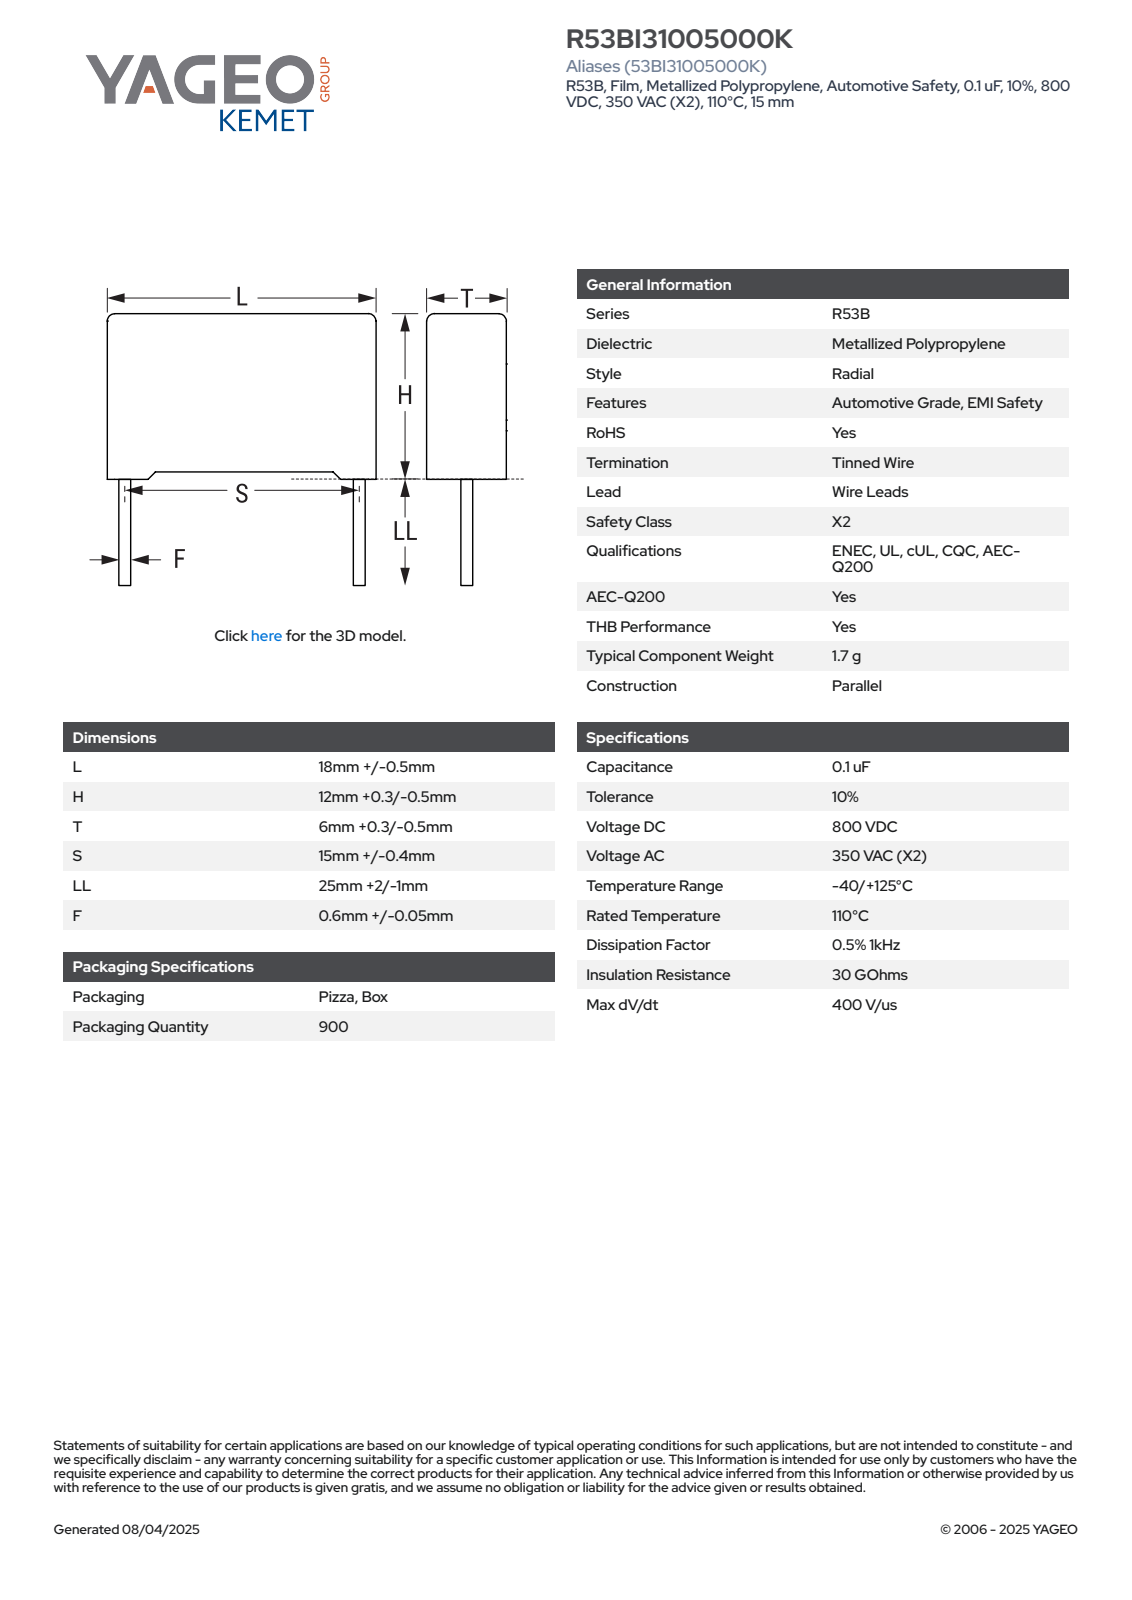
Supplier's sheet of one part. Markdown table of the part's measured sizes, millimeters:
| quantity | value |
| --- | --- |
| part name | CFR_RB2_18X12X6_L18.5H12.3T6.3S15LL27F0.65 |
| STEP written by | SolidWorks 2021 (AUTOMOTIVE_DESIGN) |
| units | millimeters |
| bodies | 4 solids, 85 faces (77 planar, 8 cylindrical, 0 other) |
| overall size | 39.3 × 18.5 × 6.3 |
| volume | 1 378 mm³ |
| surface area | 986 mm² |
| round bosses / shafts (diameter × count) | 0.65 × 2 |
| partial cylindrical surfaces (radius × count) | 0.5 × 4 |
| main face-to-face distances | 6.3, 11.55, 18.5, 0.62, 5.68, 0.75, 12.3, 0.42, 0.33, 11.88 |
